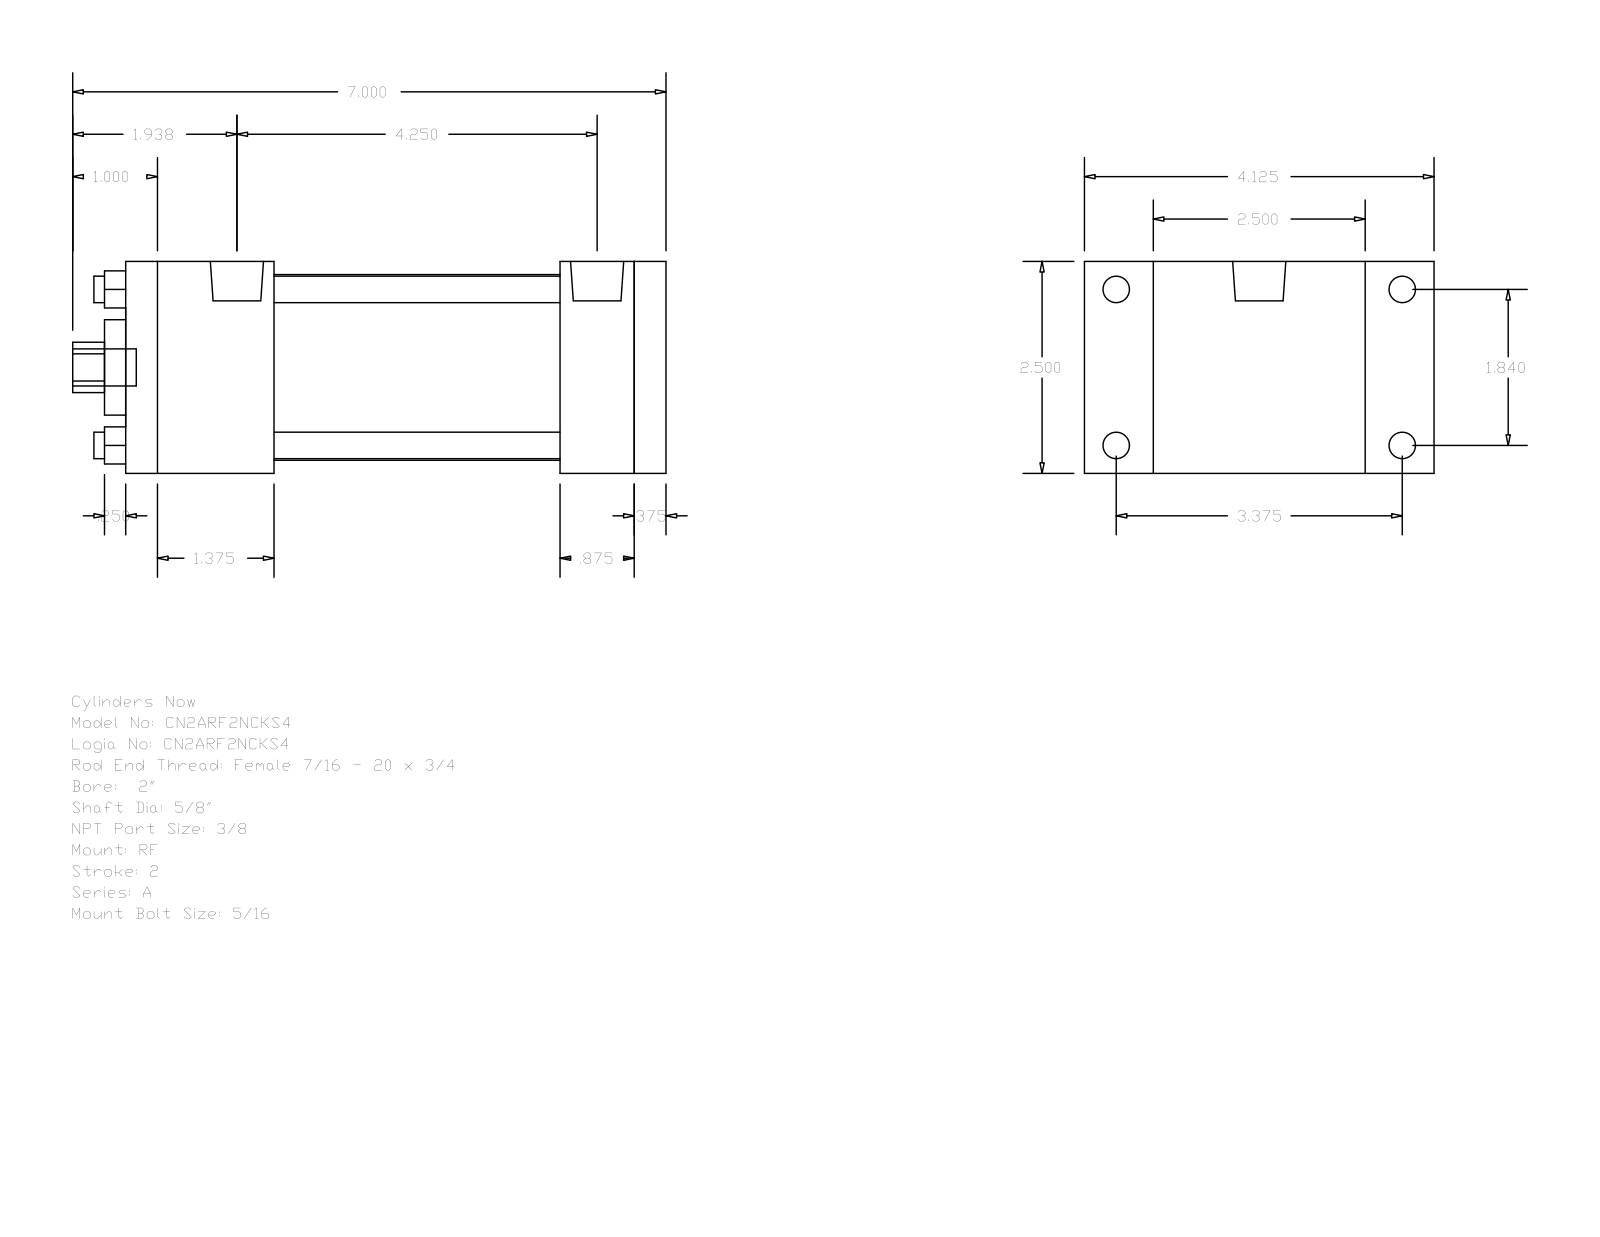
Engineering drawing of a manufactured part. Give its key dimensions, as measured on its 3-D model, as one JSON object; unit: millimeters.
{"part_name": "A_RF__0200_0.625", "step_written_by": "GSSL Pune (CONFIG_CONTROL_DESIGN)", "units": "millimeters", "bodies": {"solids": 0, "faces": 92, "planar": 64, "cylindrical": 28, "other": 0}, "overall_size": [177.8, 104.78, 63.5], "round_holes": [[7.94, 4], [15.88, 1], [28.57, 1], [55.63, 1]], "round_bosses_or_shafts": [[7.94, 4], [5.56, 4], [15.93, 2], [11.11, 1]], "partial_cylinders_radius": [[7.54, 1]], "face_to_face_distances": [63.5, 161.92, 9.52, 152.4, 44.45, 107.95, 117.47, 130.17, 85.72, 22.23], "hole_center_spacings": [33.05, 46.74, 66.1]}
